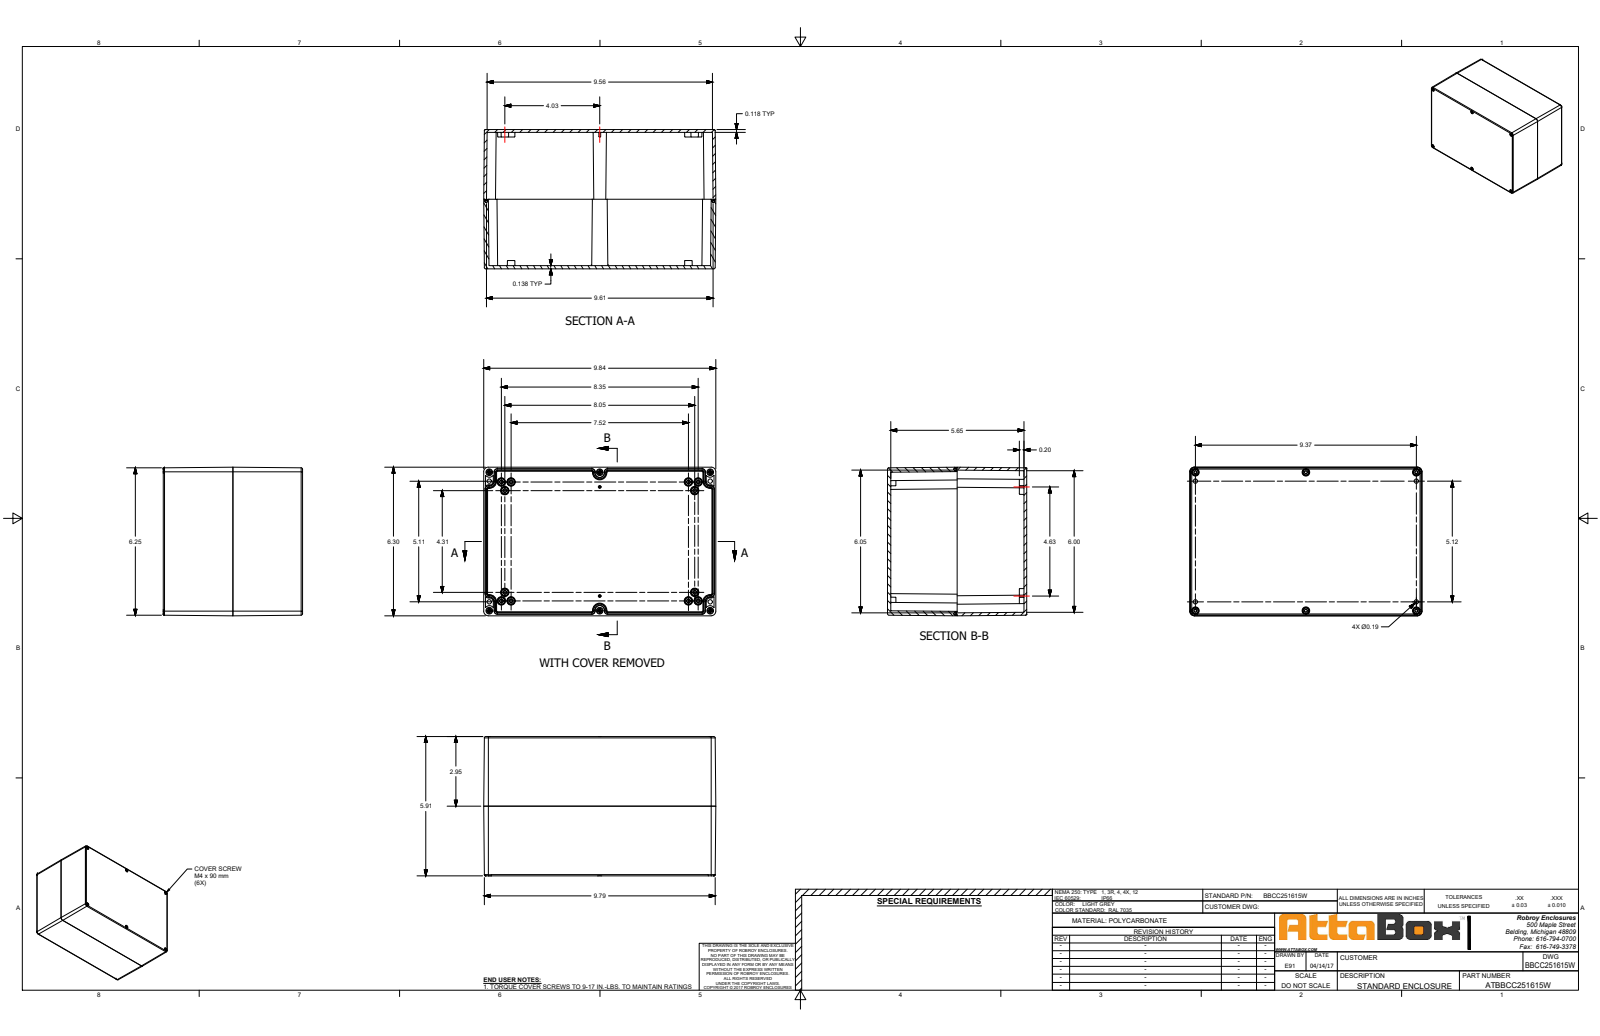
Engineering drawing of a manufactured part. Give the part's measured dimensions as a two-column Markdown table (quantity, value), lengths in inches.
| quantity | value |
| --- | --- |
| part name | BBCC251615W |
| STEP written by | SolidWorks 2018 (AUTOMOTIVE_DESIGN) |
| units | inches |
| bodies | 15 solids, 2307 faces (907 planar, 626 cylindrical, 774 other) |
| overall size | 9.843 × 6.299 × 5.907 |
| volume | 47.48 in³ |
| surface area | 706.3 in² |
| round holes (diameter × count) | 0.128 × 6, 0.177 × 6, 0.193 × 6, 0.201 × 6, 0.276 × 6, 0.283 × 6, 0.323 × 6, 0.185 × 4 |
| round bosses / shafts (diameter × count) | 0.173 × 6, 0.157 × 6, 0.13 × 6 |
| partial cylindrical surfaces (radius × count) | 0.049 × 40, 0.02 × 30, 0.039 × 20, 0.167 × 18, 0.059 × 16, 0.004 × 12, 0.102 × 6, 0.124 × 6 |
| main face-to-face distances | 0.118, 5.906, 6.299, 5.787, 0.138, 5.768, 5.65, 6.112, 6.175, 0.124 |
| hole center spacings | 0.374, 4.685, 4.7, 5.492, 7.219, 7.507, 9.37, 9.378 |
